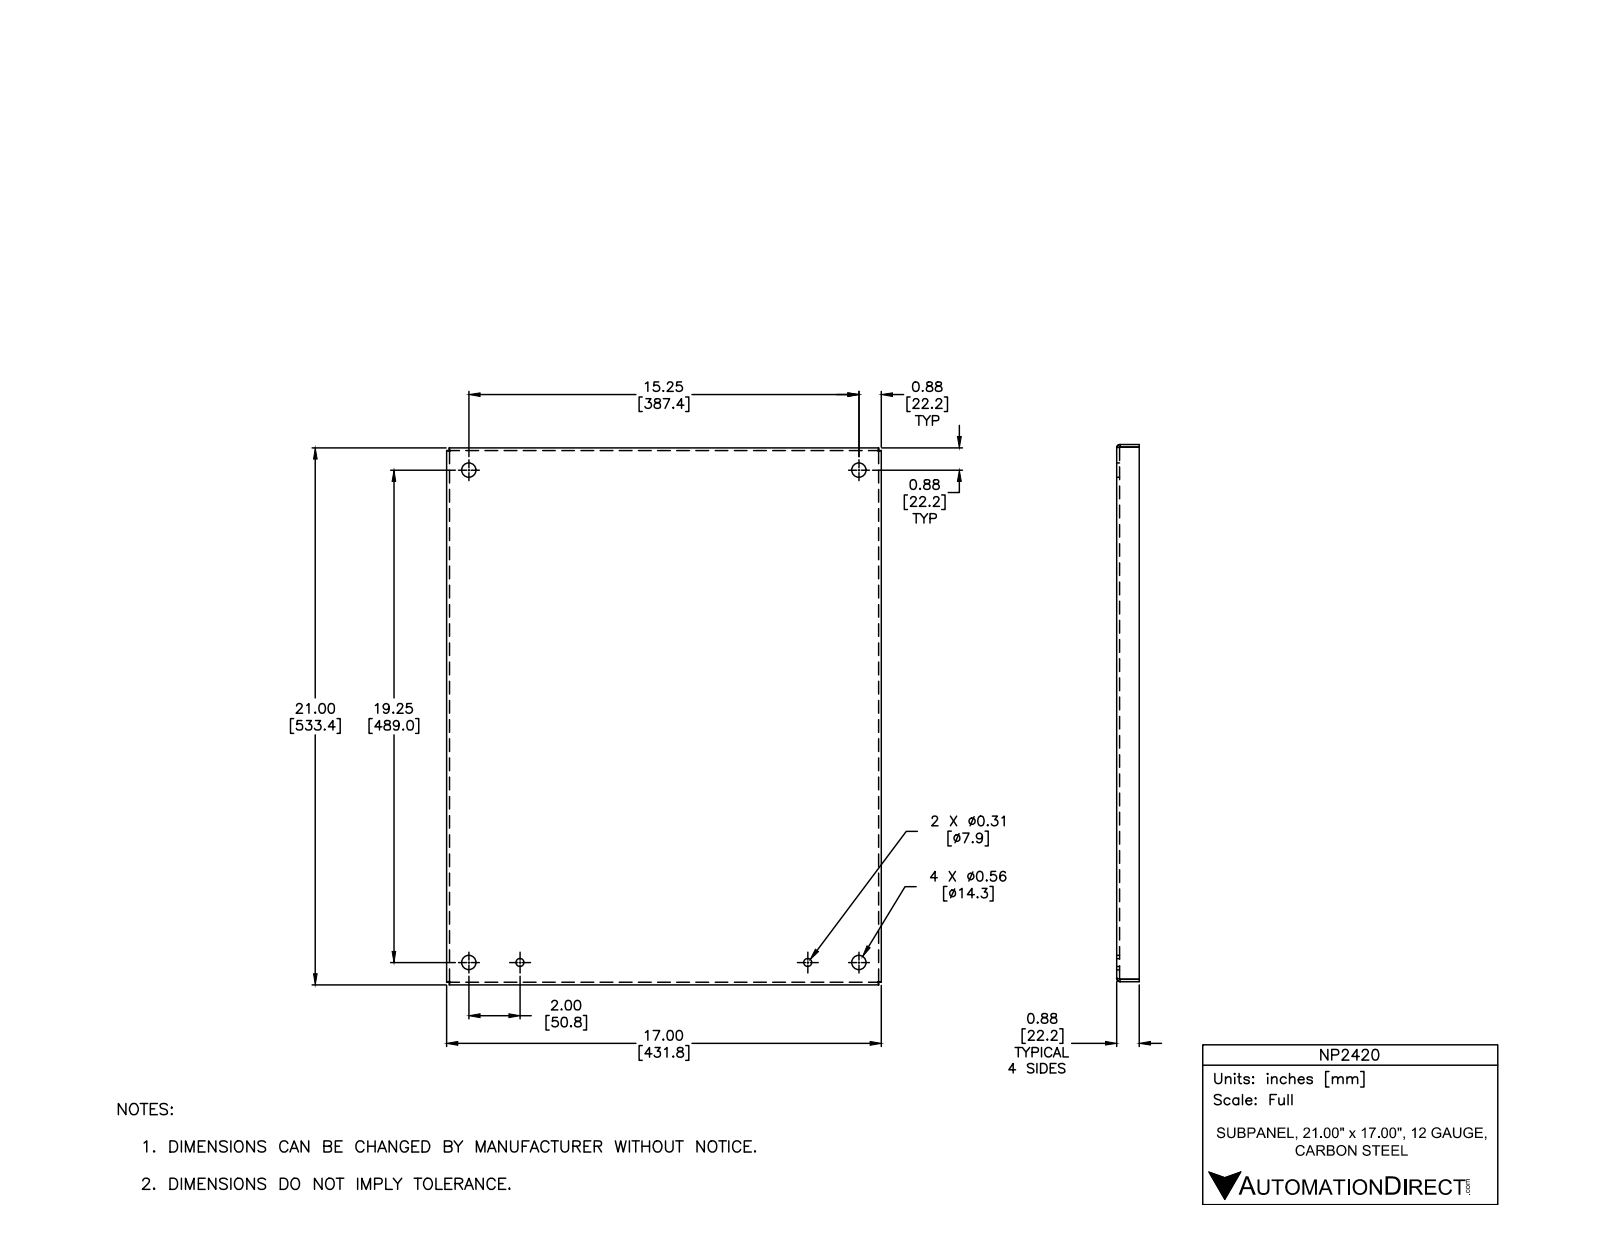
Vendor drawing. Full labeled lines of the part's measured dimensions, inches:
Part name (STEP PRODUCT): NP2420
STEP written by: Autodesk Inventor 2012 (AUTOMOTIVE_DESIGN)
Units: inches
Bodies: 1 solid, 44 faces (22 planar, 14 cylindrical, 8 other)
Overall size (bounding box): 21 × 17 × 0.875
Volume: 38.62 in³ · Surface area: 832.5 in²
Round holes (diameter × count): ⌀0.563 ×4, ⌀0.312 ×2
Partial cylindrical surfaces — rounded edges, fillets, slot ends (radius × count): R0.031 ×4, R0.125 ×4
Main face-to-face distances: 0.094, 16.906, 20.906, 17, 16.813, 21, 20.813, 0.781, 0.875, 0.105
Hole centre spacings: 15.25, 19.25, 19.354, 24.559, 2, 2, 11.25, 13.25
